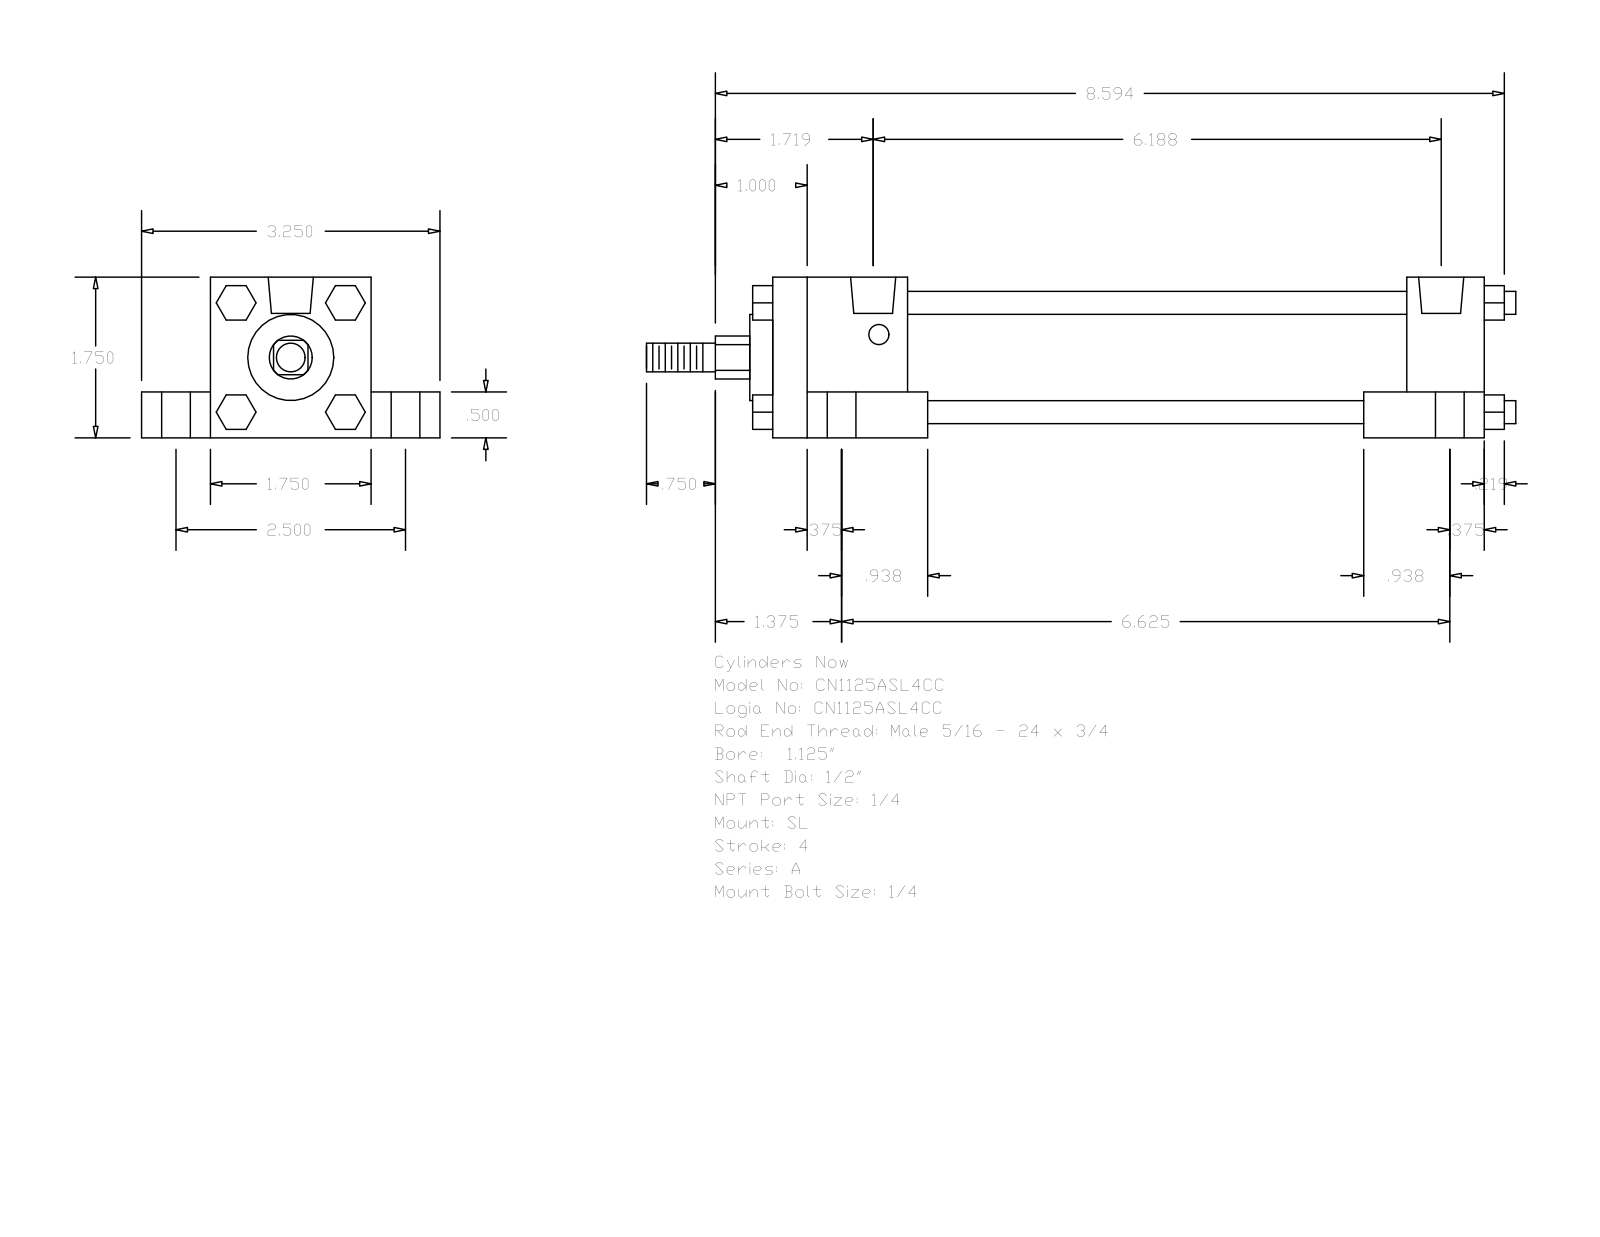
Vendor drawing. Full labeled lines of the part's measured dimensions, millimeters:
Part name (STEP PRODUCT): A_SL__0112_0.5
STEP written by: GSSL Pune (CONFIG_CONTROL_DESIGN)
Units: millimetres
Bodies: 0 solids, 150 faces (114 planar, 36 cylindrical, 0 other)
Overall size (bounding box): 240.51 × 82.55 × 44.45
Round holes (diameter × count): ⌀5.56 ×4, ⌀7.94 ×4, ⌀14.29 ×4, ⌀12.49 ×2
Round bosses / shafts (diameter × count): ⌀6.35 ×4, ⌀31.88 ×1, ⌀23.81 ×1, ⌀12.7 ×1, ⌀7.94 ×1
Partial cylindrical surfaces — rounded edges, fillets, slot ends (radius × count): R5.94 ×1
Main face-to-face distances: 44.46, 31.76, 12.7, 19.04, 63.5, 159.54, 196.84, 175.41, 21.43, 37.3
Hole centre spacings: 31.84, 32, 32.93, 33.39, 63.5, 153.99, 161.12, 162.67
